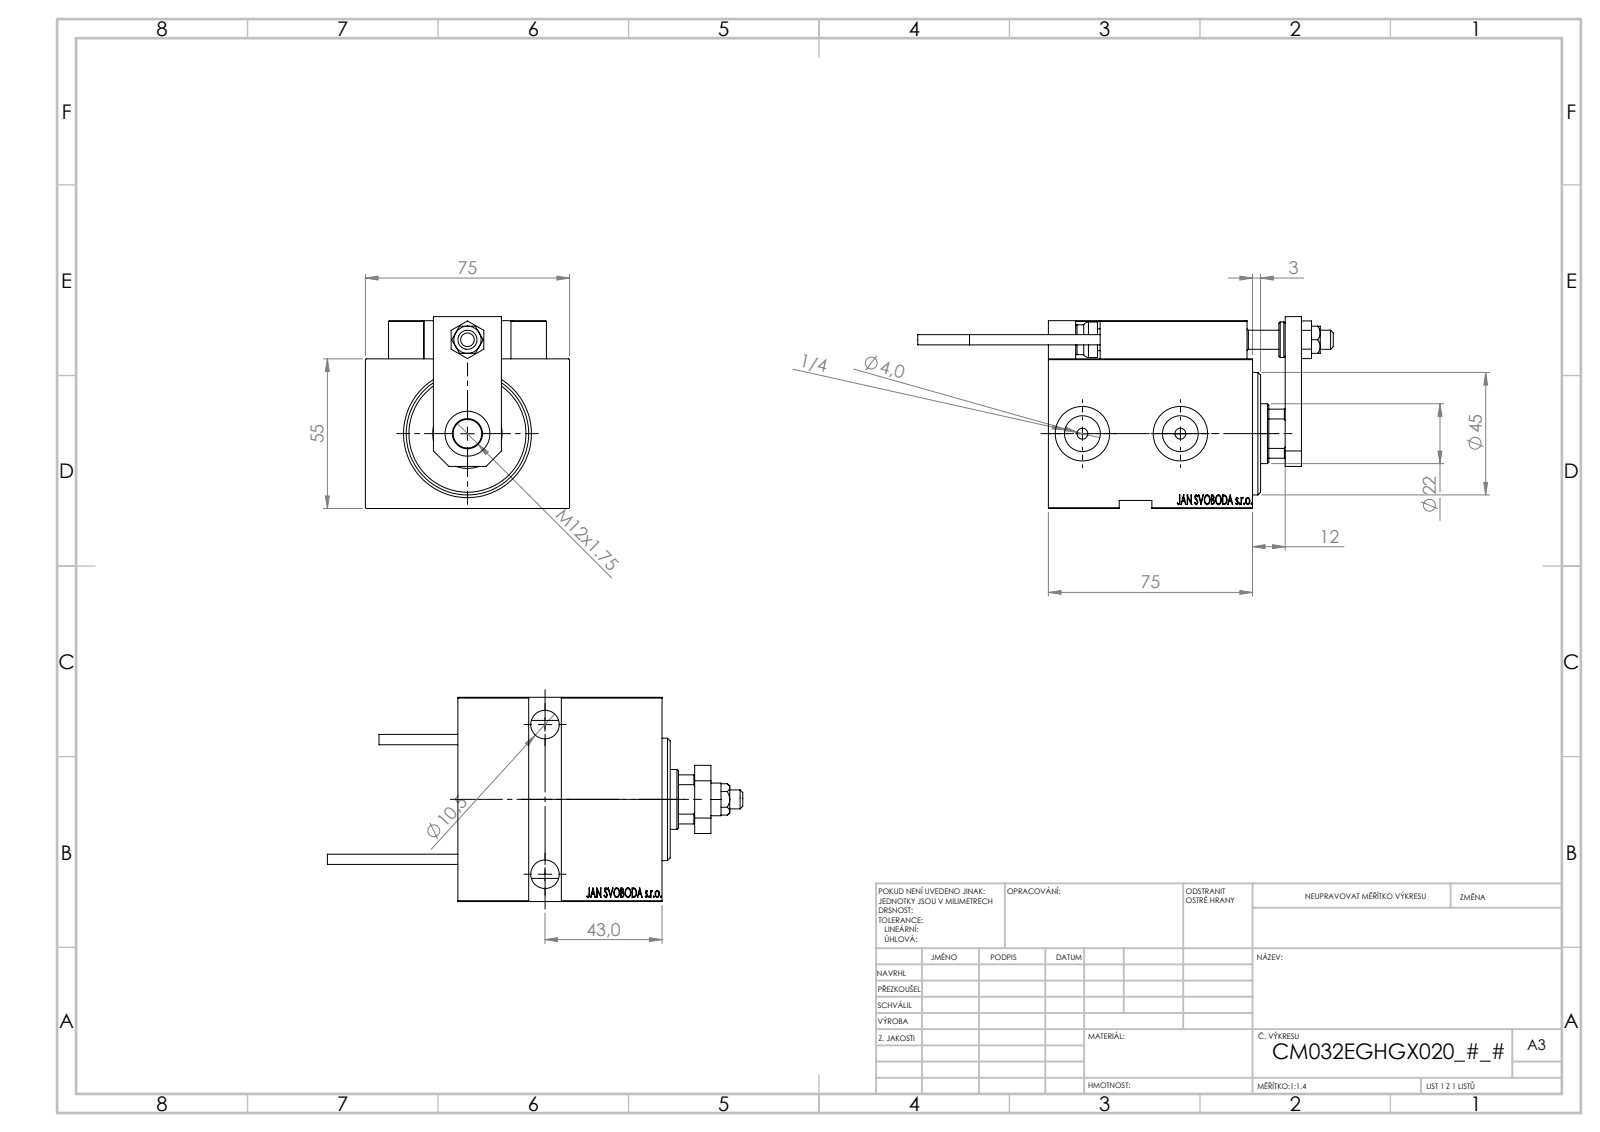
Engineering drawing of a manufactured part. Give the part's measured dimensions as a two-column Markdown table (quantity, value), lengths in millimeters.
| quantity | value |
| --- | --- |
| part name | NUT_D10; Block; KONCOVKA; V450CM_E_VCP (+8 more) |
| STEP written by | SolidWorks 2019 (CONFIG_CONTROL_DESIGN) |
| units | millimeters |
| bodies | 24 solids, 1283 faces (568 planar, 174 cylindrical, 541 other) |
| overall size | 152.7 × 75 × 70.5 |
| volume | 330 502 mm³ |
| surface area | 78 511 mm² |
| round holes (diameter × count) | 4 × 6, 8 × 5, 3.2 × 4, 10.5 × 3, 16.5 × 3, 5 × 2, 13.16 × 2, 20 × 2, 7 × 1, 22 × 1, 25.5 × 1, 32 × 1 |
| round bosses / shafts (diameter × count) | 5 × 2, 3.8 × 2, 13 × 1, 11 × 1 |
| partial cylindrical surfaces (radius × count) | 0.3 × 30, 3 × 2, 10.5 × 1 |
| main face-to-face distances | 75, 55, 10, 14, 3, 65, 69, 12, 25, 5 |
| hole center spacings | 11.37, 20, 27.07, 29.59, 29.69, 32.18, 34.83, 36.06 |
